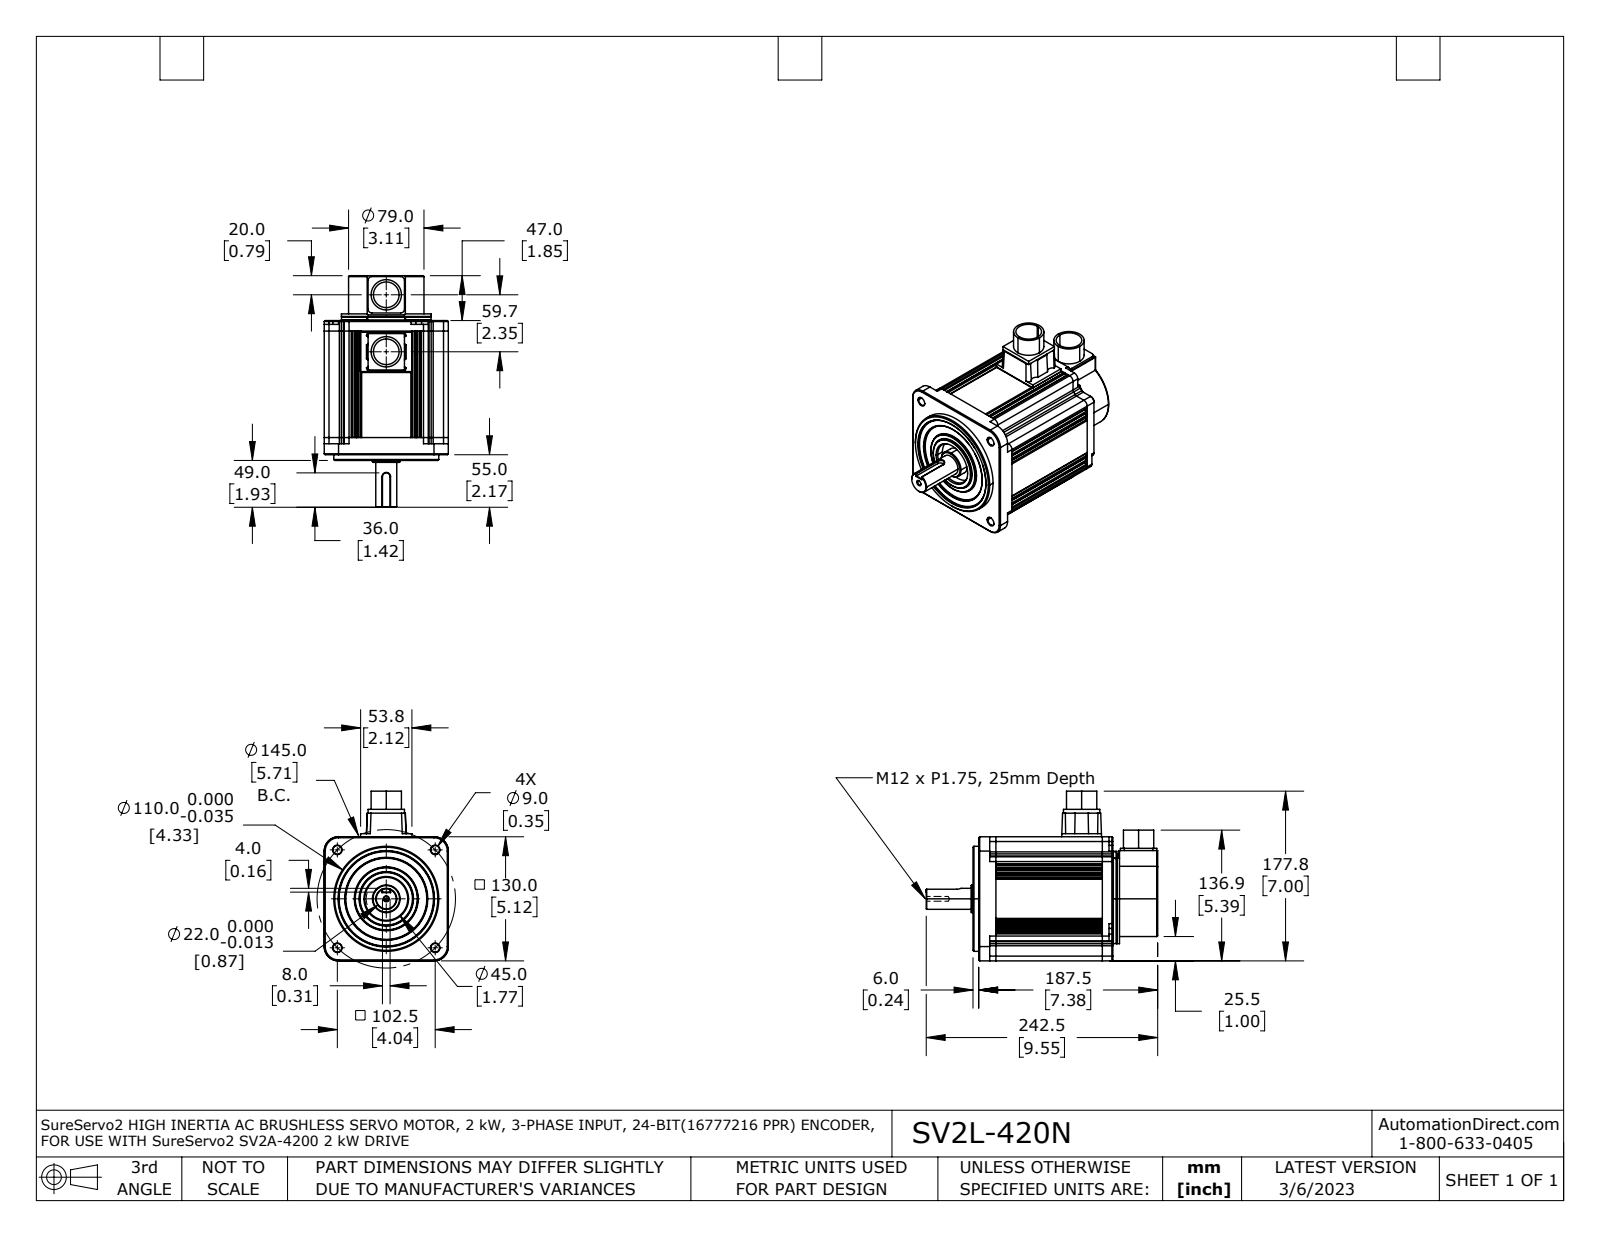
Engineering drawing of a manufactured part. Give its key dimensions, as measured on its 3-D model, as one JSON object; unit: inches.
{"part_name": "SV2L-420N r1", "step_written_by": "SolidWorks 2021 (AUTOMOTIVE_DESIGN)", "units": "inches", "bodies": {"solids": 1, "faces": 586, "planar": 270, "cylindrical": 156, "other": 160}, "overall_size": [9.547, 6.998, 5.118], "volume_in3": 152.2, "surface_area_in2": 239.2, "round_holes": [[0.354, 4], [1.058, 2], [0.197, 1], [1.772, 1], [3.386, 1], [3.937, 1]], "round_bosses_or_shafts": [[1.25, 2], [4.331, 1], [3.701, 1], [3.11, 1], [2.598, 1], [2.205, 1], [1.142, 1], [0.866, 1]], "partial_cylinders_radius": [[0.039, 70], [0.02, 10], [0.157, 9], [0.118, 8], [0.197, 8]], "face_to_face_distances": [0.827, 4.291, 5.118, 2.402, 5.531, 0.211, 0.959, 1.85, 7.382, 3.465], "hole_center_spacings": [2.855, 4.037, 5.709, 2.35]}
